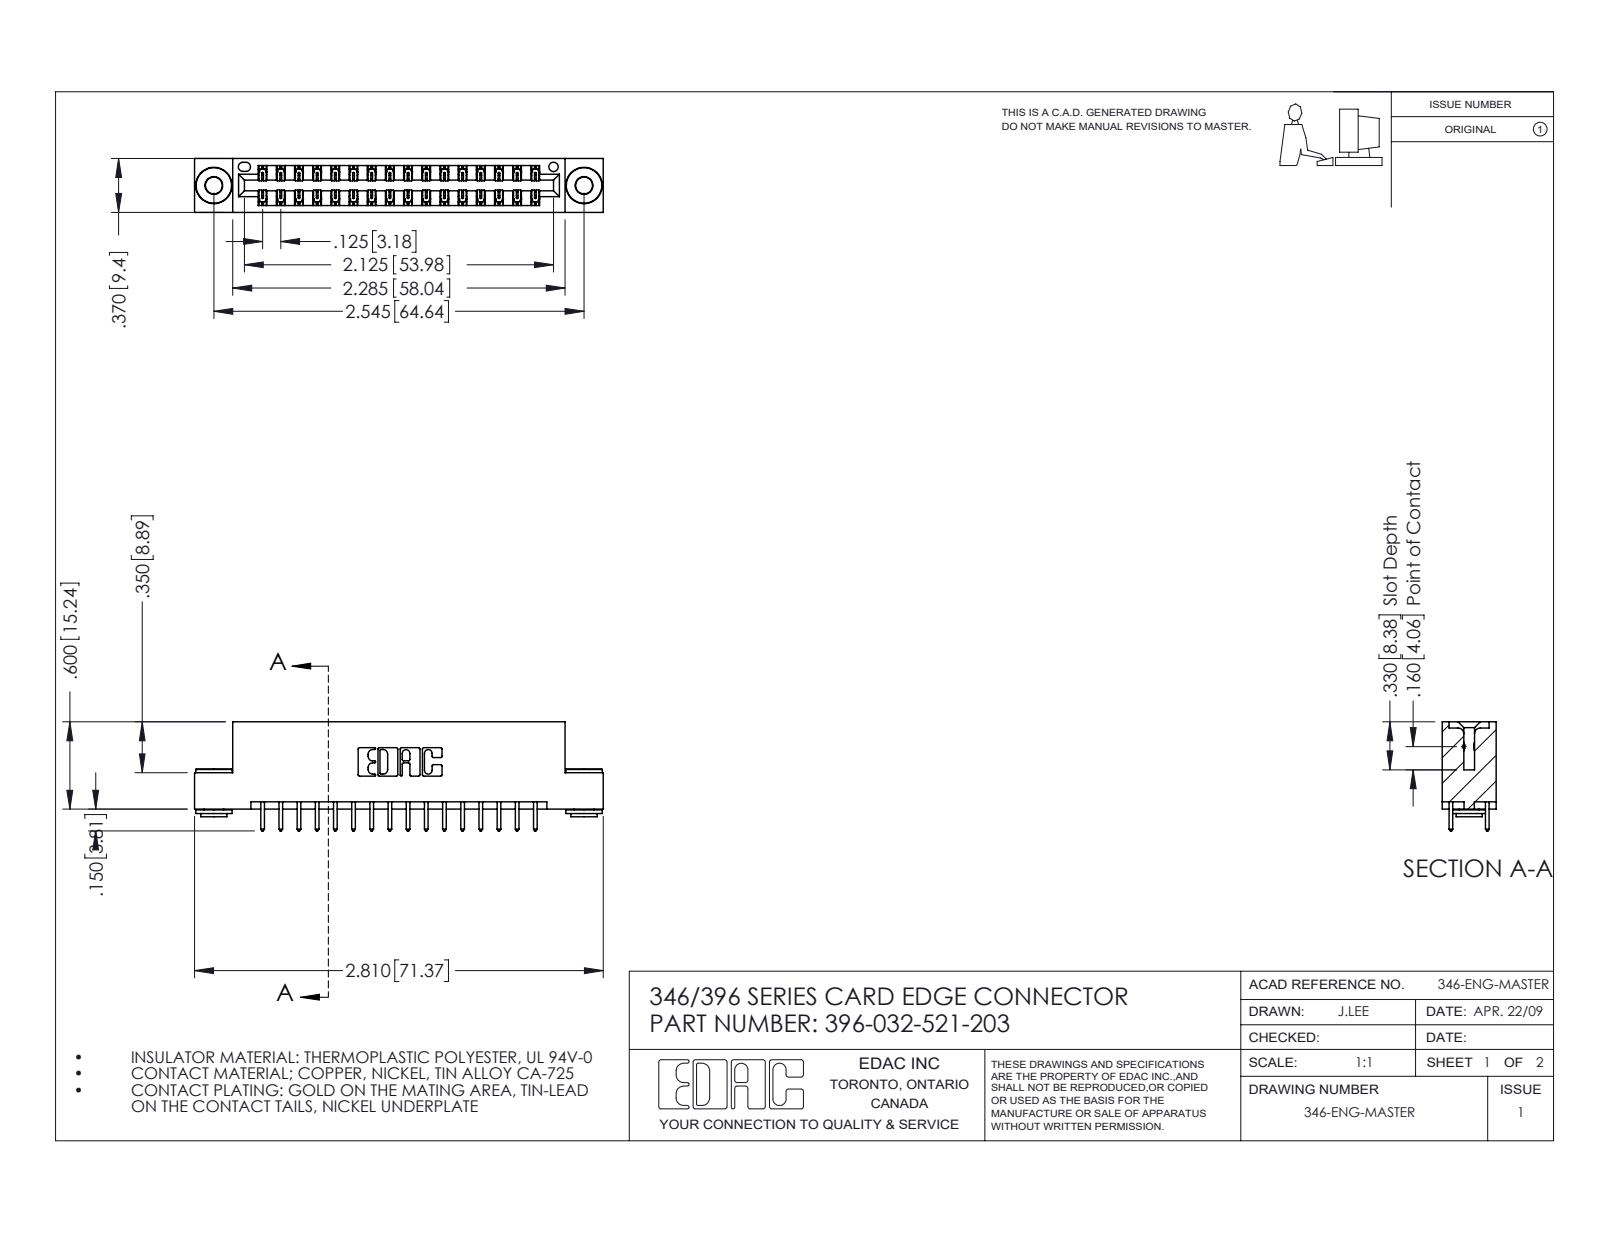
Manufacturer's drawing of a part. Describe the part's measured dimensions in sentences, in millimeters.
The part is named "345-292-001_345-293-121; 346 Part_Flush Mounting Lugs - 0.156 Dia-TH; 396-032-521-203; 345-250-002_345-250-002-102". Its 3-D file was written by "SolidWorks 2016 (CONFIG_CONTROL_DESIGN)". It is 35 solids with 1824 faces: 1206 planar, 610 cylindrical and 8 other. Overall it measures 71.4 by 19.1 by 9.4 millimeters. Its volume is 6 770 cubic millimeters and its surface area 9 013 square millimeters. Round holes: 2 of diameter 2.9, 2 of diameter 4, 1 of diameter 1.6. Round bosses or shafts: 2 of diameter 6.4, 2 of diameter 4.6, 2 of diameter 3.5. Partial cylindrical surfaces (rounded edges, fillets, slot ends): 48 of radius 0.2, 32 of radius 0.3, 22 of radius 0.3, 6 of radius 0.2, 6 of radius 0.8, 3 of radius 0.7, 2 of radius 0.4, 2 of radius 0.6. The main face-to-face distances are 1.2, 8.2, 6.4, 9.4, 0.6, 1.8, 7.6, 7, 3.8, 5.6. The hole center spacings are 6.2, 59.4, 64.6.
